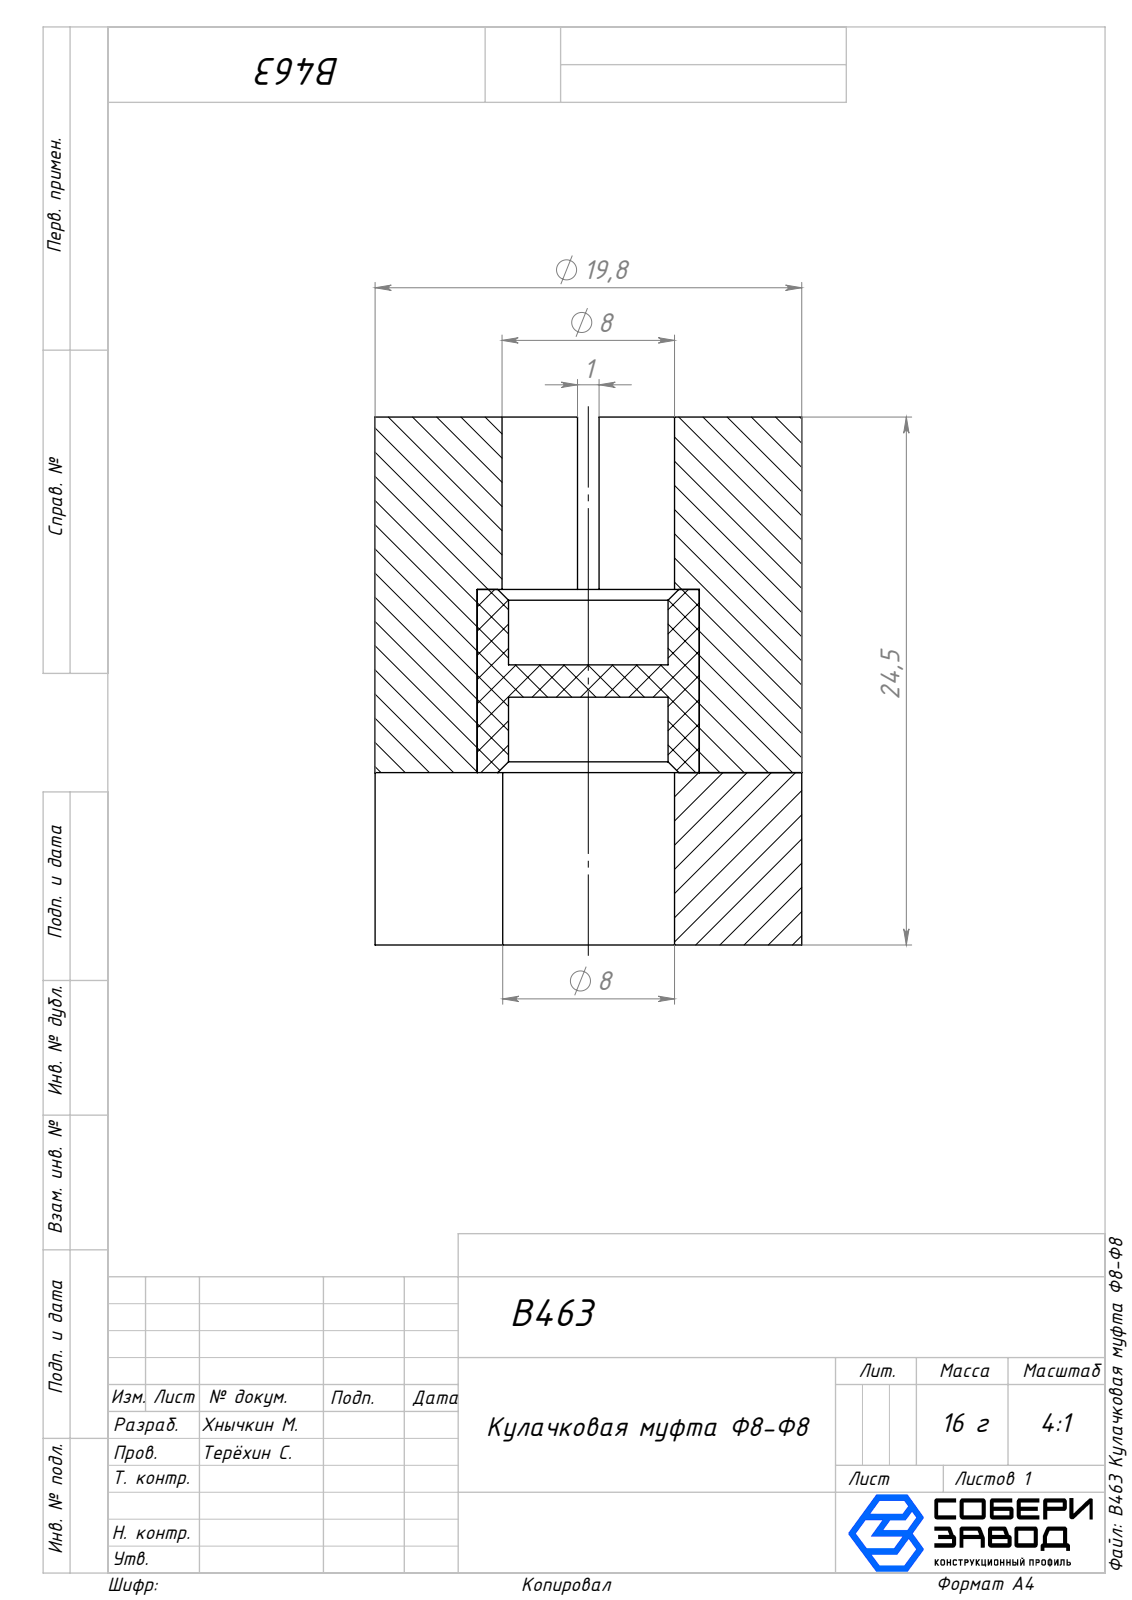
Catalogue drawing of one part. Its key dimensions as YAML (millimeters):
part_name: "Низ_00; Середина_00; B463 Кулачковая муфта Ф8-Ф8; Верх_00"
step_written_by: "SolidWorks 2025 (AUTOMOTIVE_DESIGN)"
units: millimeters
bodies: {solids: 3, faces: 56, planar: 24, cylindrical: 28, other: 4}
overall_size: [24.5, 19.8, 19.8]
volume: 6338
surface_area: 4518
round_holes:
  - {diameter: 7.4, count: 1}
  - {diameter: 8, count: 1}
round_bosses_or_shafts:
  - {diameter: 19.8, count: 1}
partial_cylinders:
  - {radius: 6, count: 8}
face_to_face_distances: [8, 16.5, 8.5, 24.5, 4.65, 5.65, 1, 11.5, 13, 3.5]
